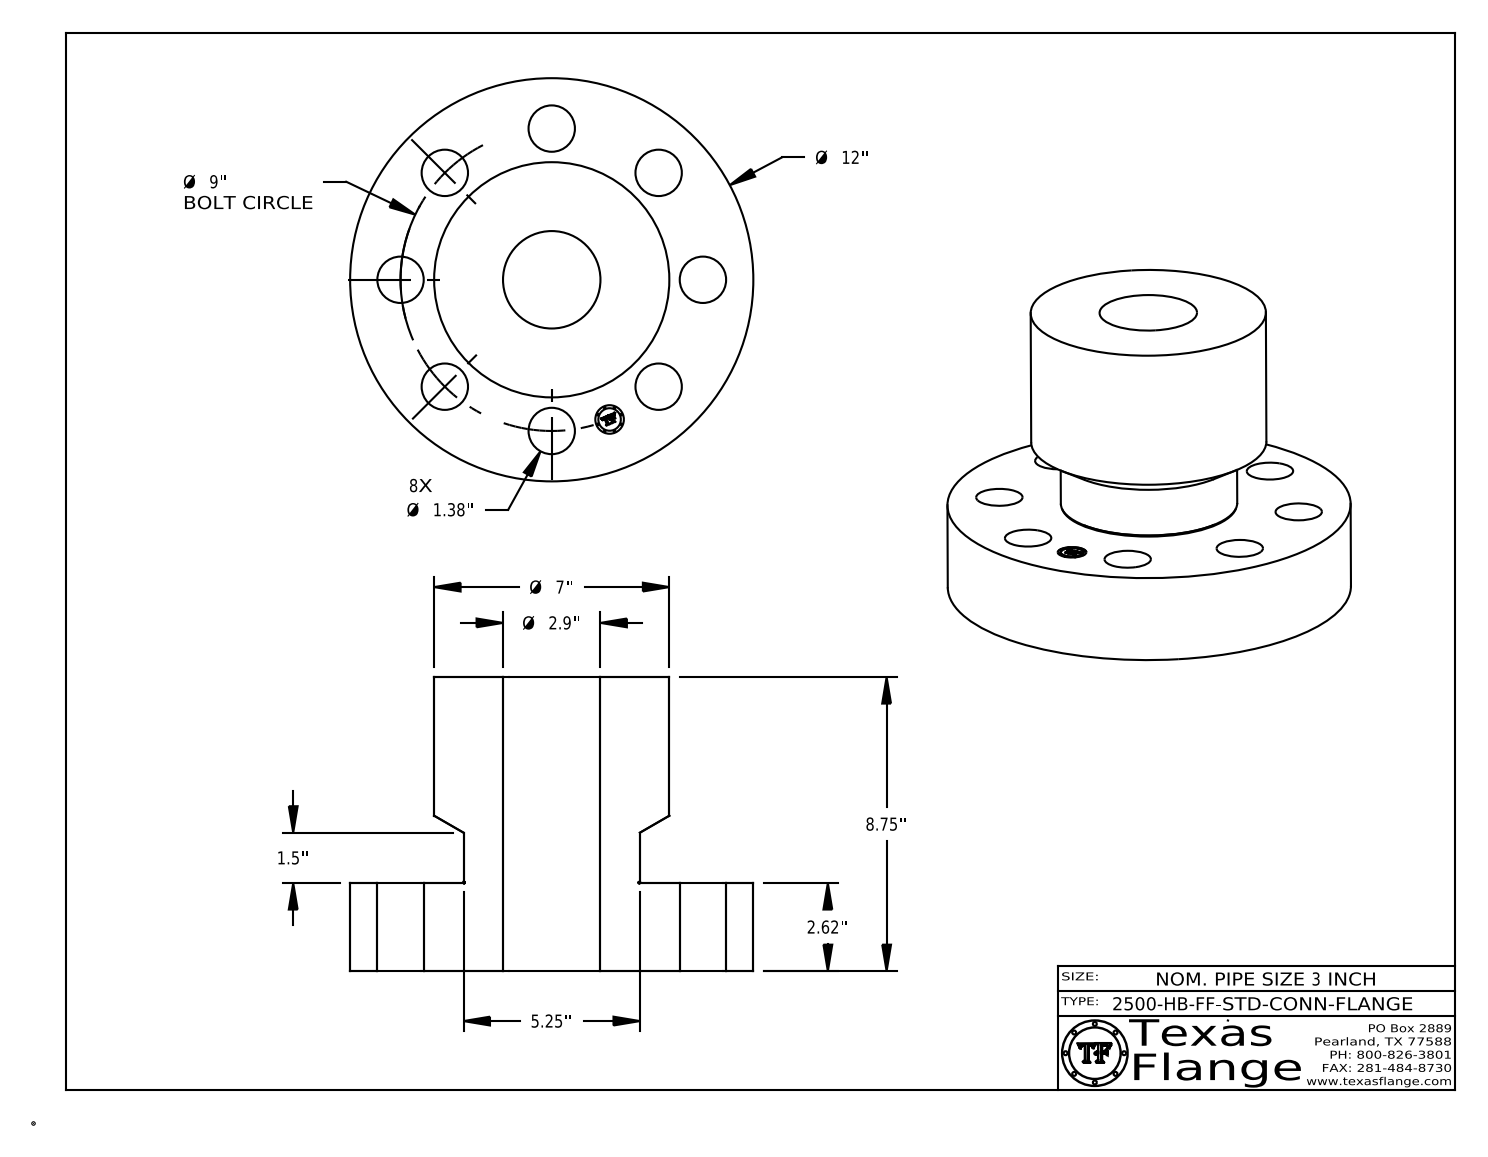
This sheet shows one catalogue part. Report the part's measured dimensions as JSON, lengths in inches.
{"part_name": "3-2500-HB-FF-STD-CONN-FLANGE", "step_written_by": "CATIA V5 STEP AP214 (AUTOMOTIVE_DESIGN)", "units": "inches", "bodies": {"solids": 1, "faces": 418, "planar": 368, "cylindrical": 44, "other": 6}, "overall_size": [12, 12, 8.75], "volume_in3": 413.4, "surface_area_in2": 610.8, "round_holes": [[1.38, 8], [0.85, 1], [2.9, 1]], "round_bosses_or_shafts": [[0.051, 8], [12, 1], [7, 1], [5.25, 1], [0.67, 1]], "face_to_face_distances": [2.62, 8.75, 6.13, 2.615, 6.135, 0.254, 0.248, 0.046, 0.165, 0.211], "hole_center_spacings": [4.5, 3.444, 6.364, 8.315, 1.756, 5, 7.483, 9]}
